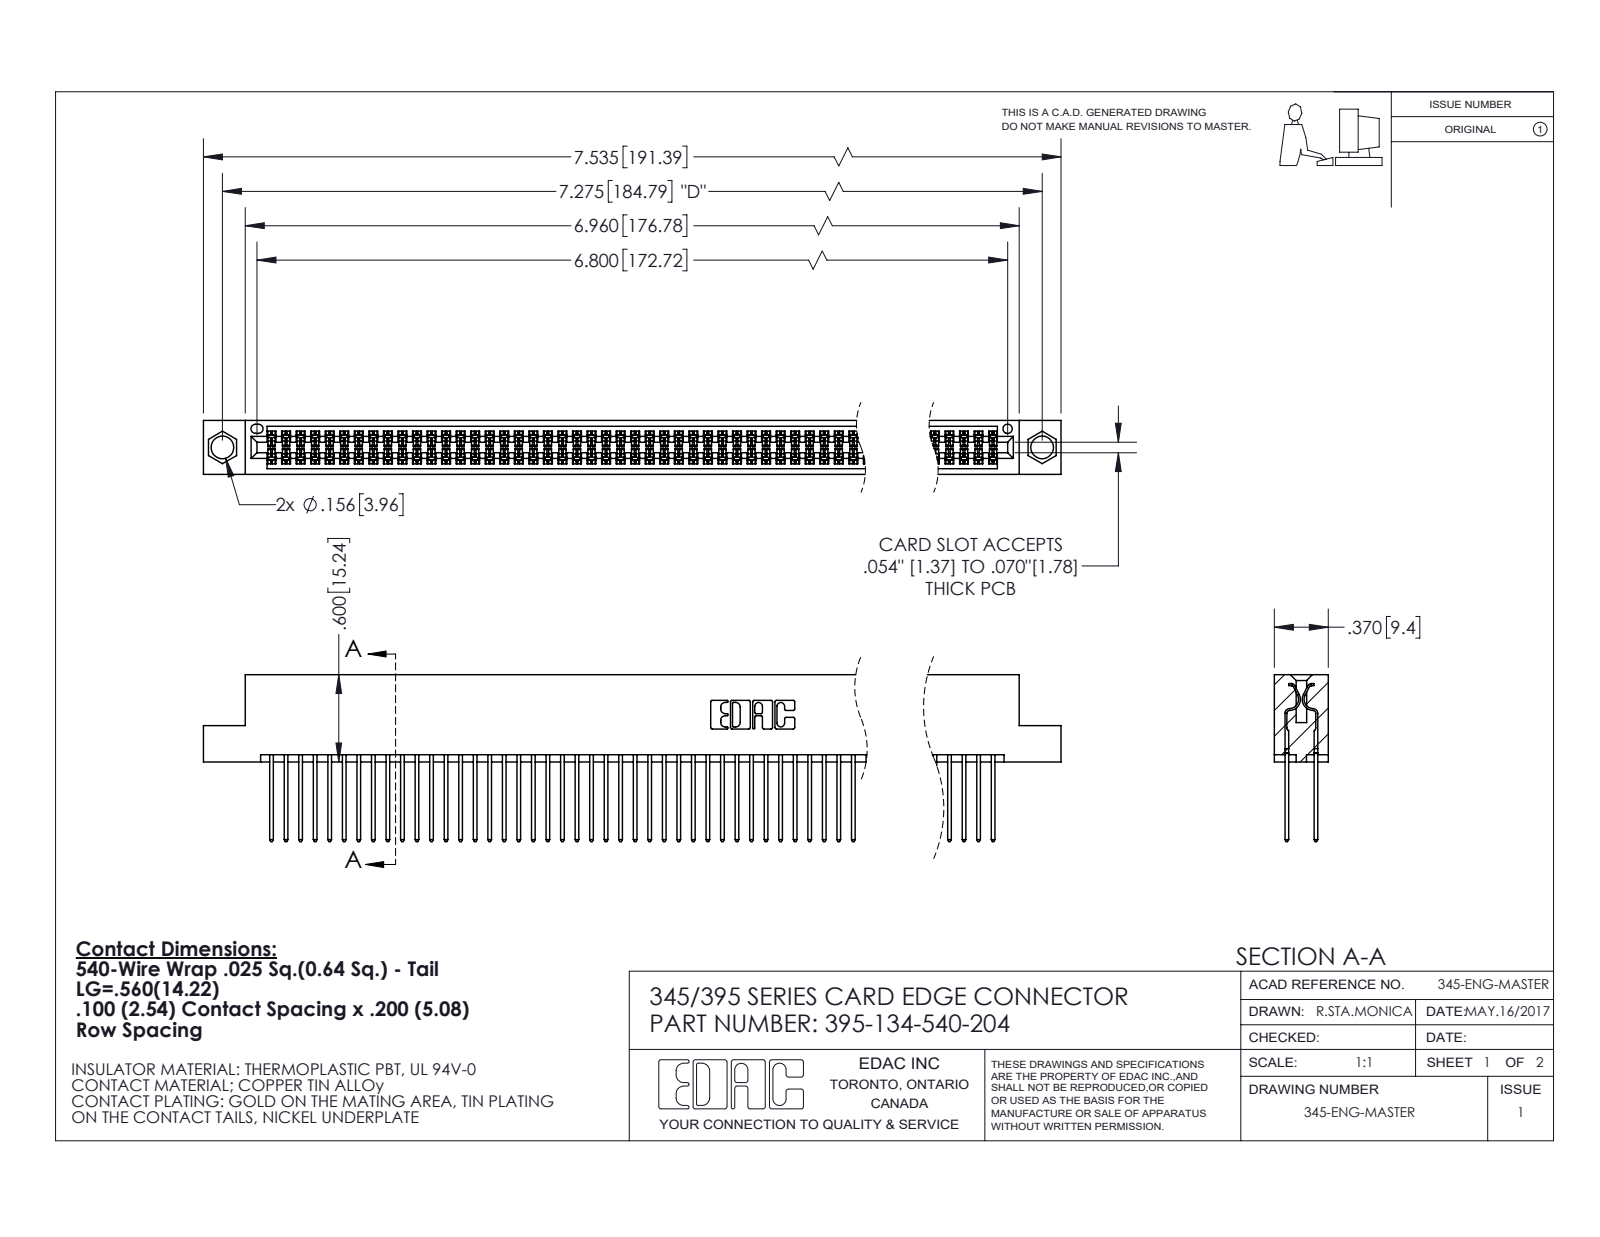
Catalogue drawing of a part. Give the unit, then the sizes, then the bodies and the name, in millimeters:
Units: millimetres
Overall size (bounding box): 191.4 × 29.1 × 9.4
Round holes (diameter × count): ⌀4 ×2, ⌀1.6 ×1
Partial cylindrical surfaces — rounded edges, fillets, slot ends (radius × count): R0.2 ×201, R0.3 ×134, R0.3 ×22, R0.2 ×6, R0.8 ×6, R0.7 ×3, R0.4 ×2, R0.5 ×2
Main face-to-face distances: 7.6, 1.8, 5.1, 2.5, 6.9, 0.6, 5.7, 9.4, 4.4, 3.8
Hole centre spacings: 6.9, 178.8, 184.8
Volume: 19 220 mm³ · Surface area: 31 110 mm²
Bodies: 135 solids, 6840 faces (4516 planar, 2324 cylindrical, 0 other)
Part name (STEP PRODUCT): 395-134-540-204; 345-292-001_345-293-140; 345 Part_Flush Mounting Lugs - 0.156 Dia-TI
STEP written by: SolidWorks 2020 (CONFIG_CONTROL_DESIGN)
